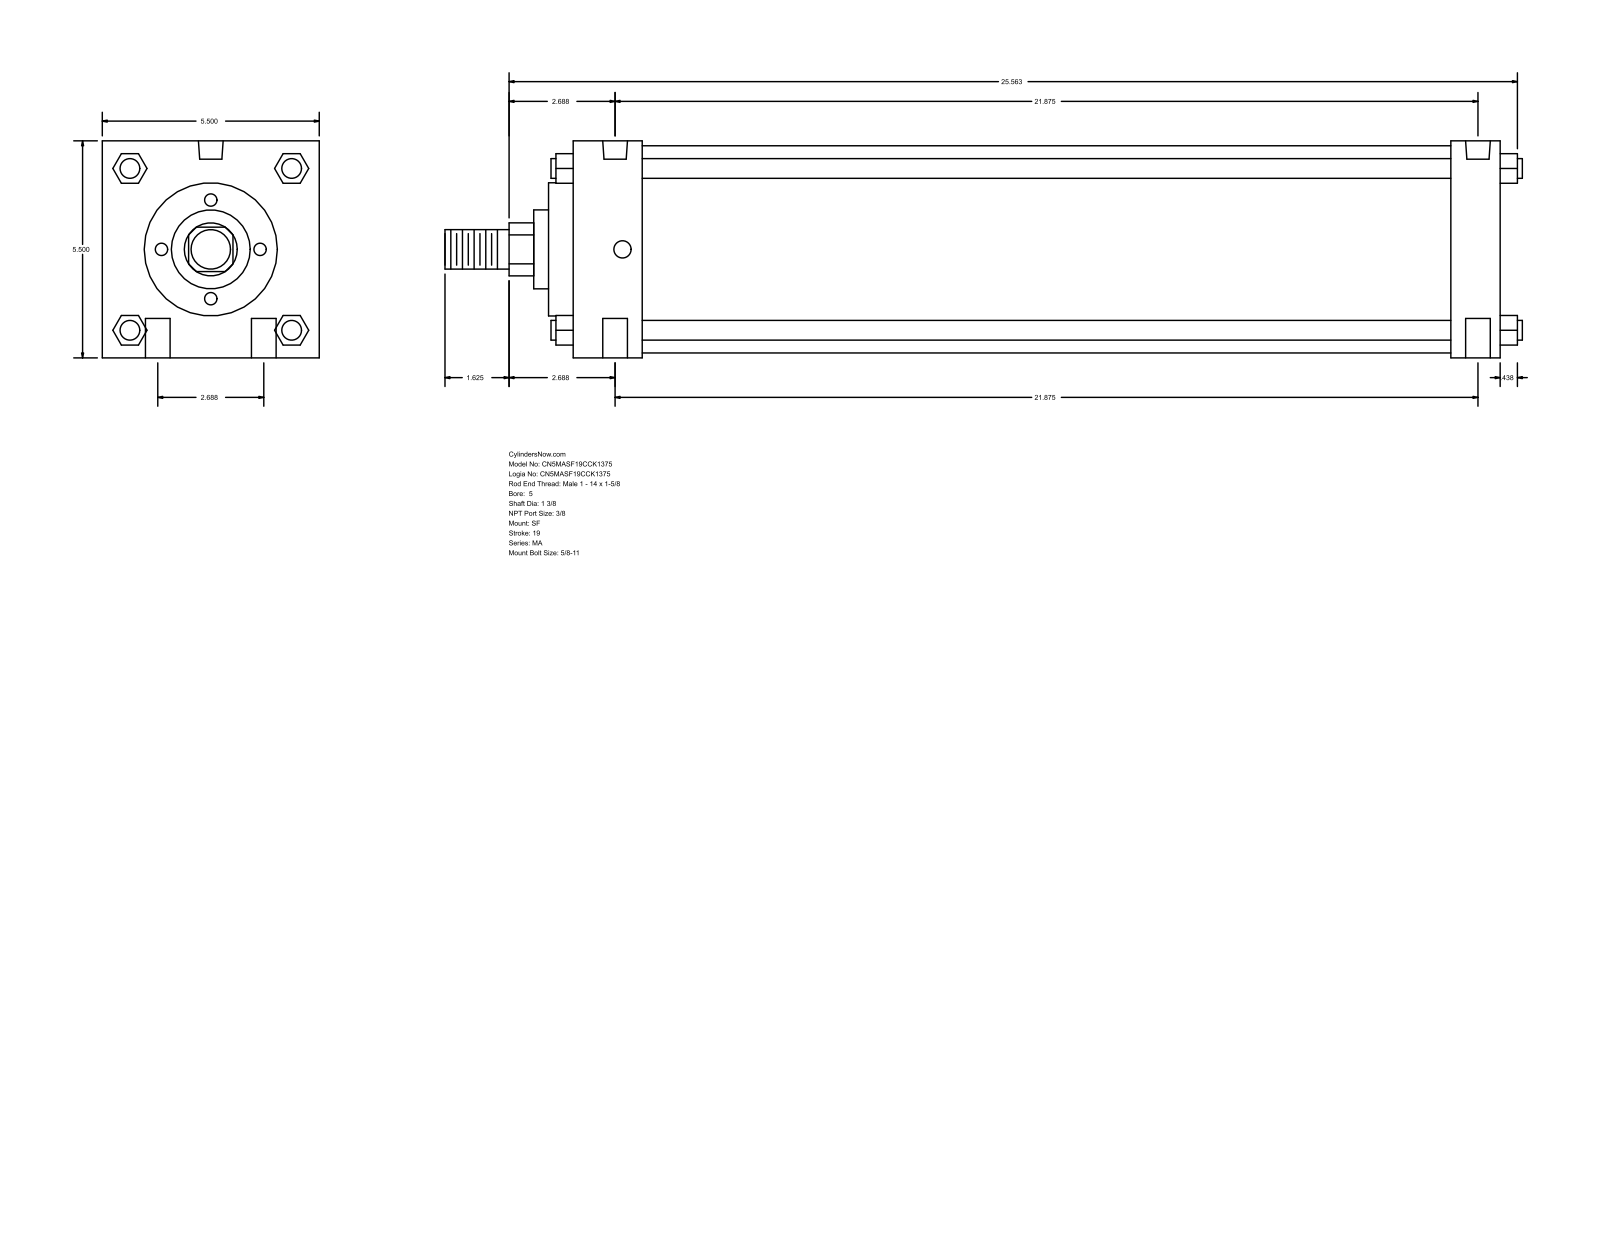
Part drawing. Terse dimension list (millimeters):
name: MA_SF__0500_1.375
written by: GSSL Pune (CONFIG_CONTROL_DESIGN)
unit: mm
bodies: 0 solids, 126 faces (95 planar, 31 cylindrical, 0 other)
size: 693.74 × 139.7 × 139.7
holes: 4× ⌀15.88, 2× ⌀11.11, 2× ⌀15.93
bosses: 4× ⌀12.7, 1× ⌀133.35, 1× ⌀85.72, 1× ⌀50.8, 1× ⌀34.92, 1× ⌀25.4
rounds: 1× R17.06
face distances: 139.7, 596.9, 44.45, 565.15, 520.7, 552.45, 31.75, 15.87, 60.32, 581.02
hole spacings: 34.13, 556.68, 555.63, 68.26, 559.81, 546.09
